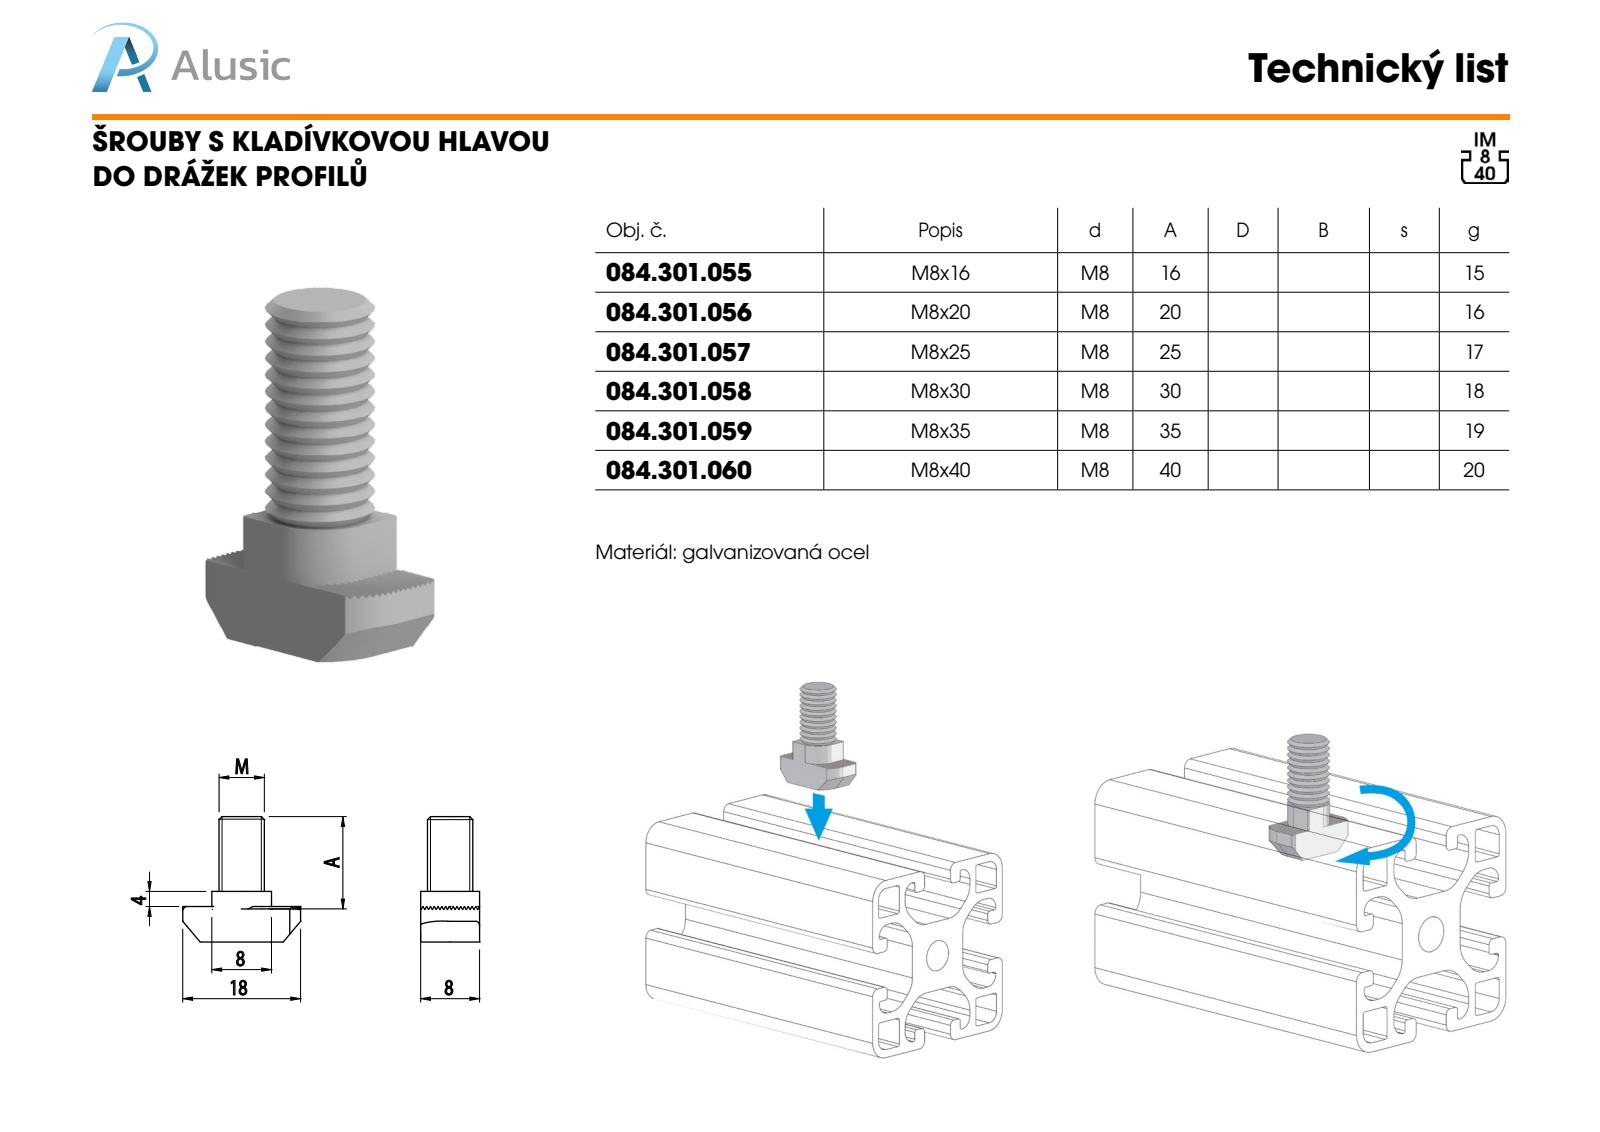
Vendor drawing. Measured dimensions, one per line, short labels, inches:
name: 084.301.055
written by: SolidWorks 2016 (CONFIG_CONTROL_DESIGN)
unit: in
bodies: 1 solid, 143 faces (108 planar, 31 cylindrical, 4 other)
size: 0.827 × 0.709 × 0.315
volume: 0.077 in³; area: 1.632 in²
bosses: 1× ⌀0.276
rounds: 2× R0.012, 2× R0.138, 2× R0.197
face distances: 0.315, 0.028, 0.014, 0.014, 0.042, 0.07, 0.042, 0.056, 0.827, 0.111
